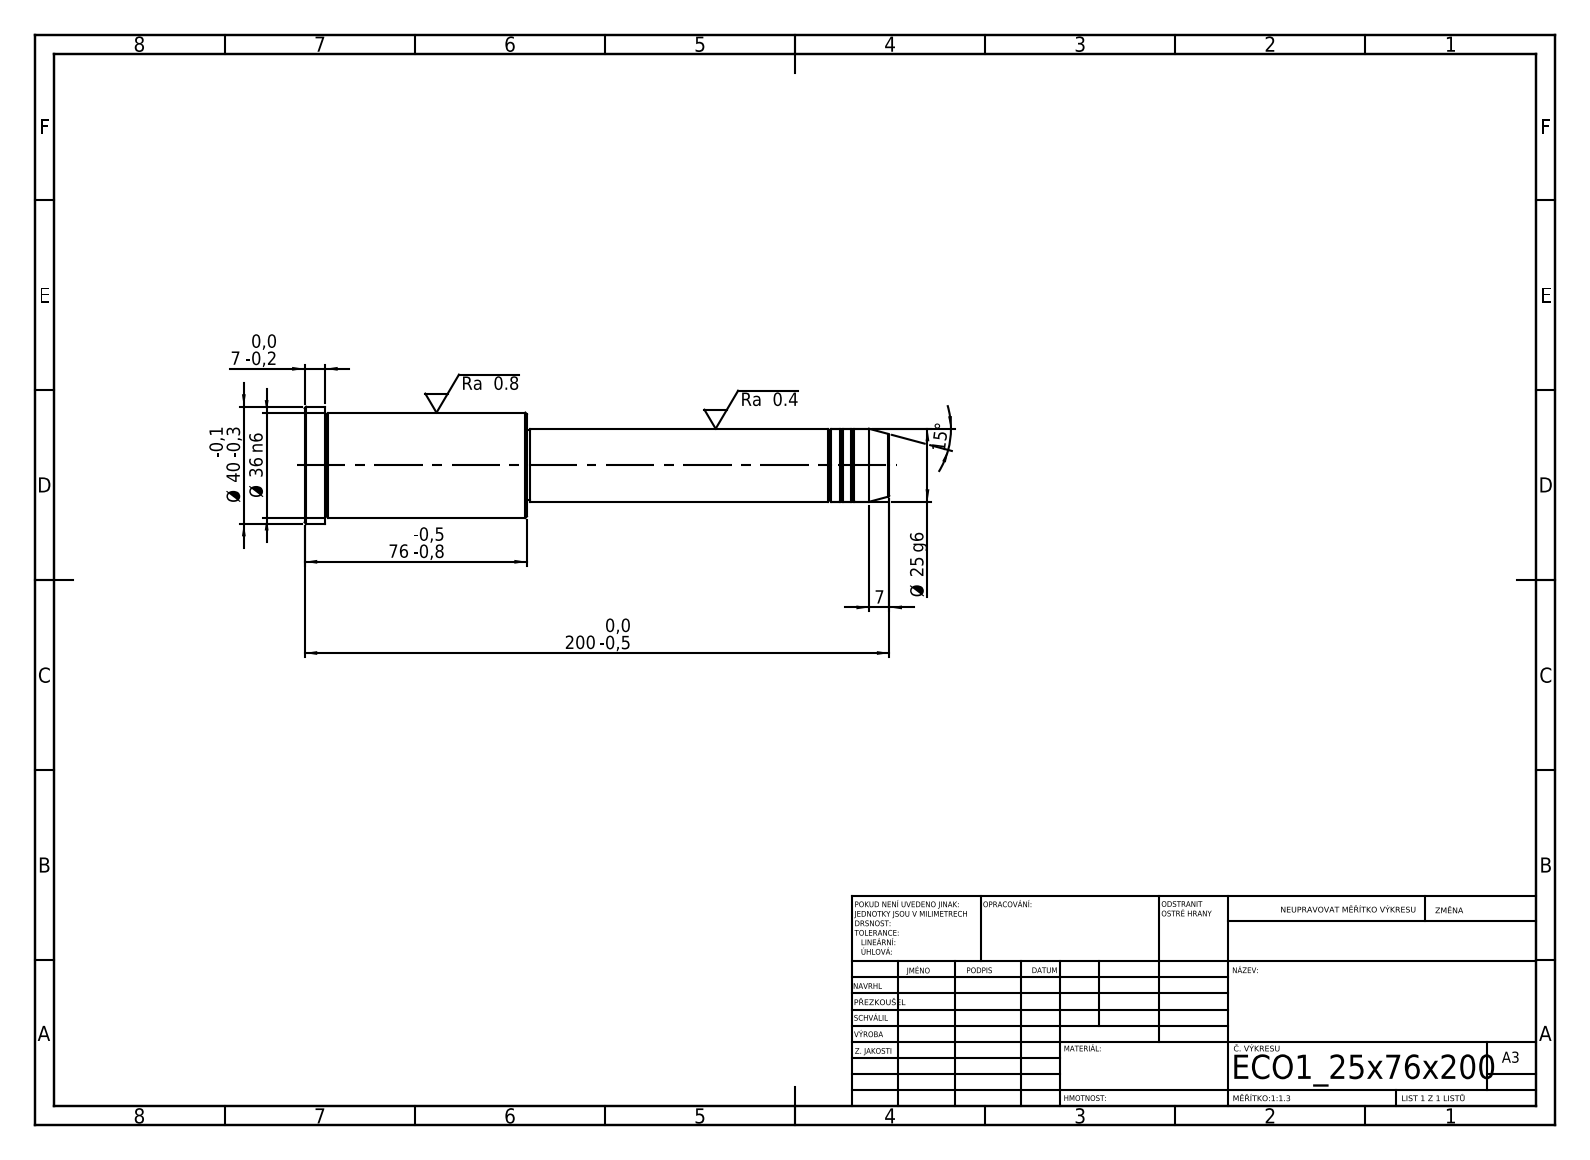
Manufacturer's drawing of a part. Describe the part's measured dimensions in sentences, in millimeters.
Its 3-D file was written by "SolidWorks 2019 (CONFIG_CONTROL_DESIGN)". It is 1 solid with 43 faces: 5 planar, 14 cylindrical and 24 other. Overall it measures 200 by 40 by 40 millimeters. Its volume is 139 204 cubic millimeters and its surface area 20 958 square millimeters. Round bosses or shafts: 1 of diameter 40, 1 of diameter 36, 1 of diameter 25, 1 of diameter 24. The main face-to-face distances are 76, 124, 200, 193, 69, 7, 123, 1, 70, 77.
